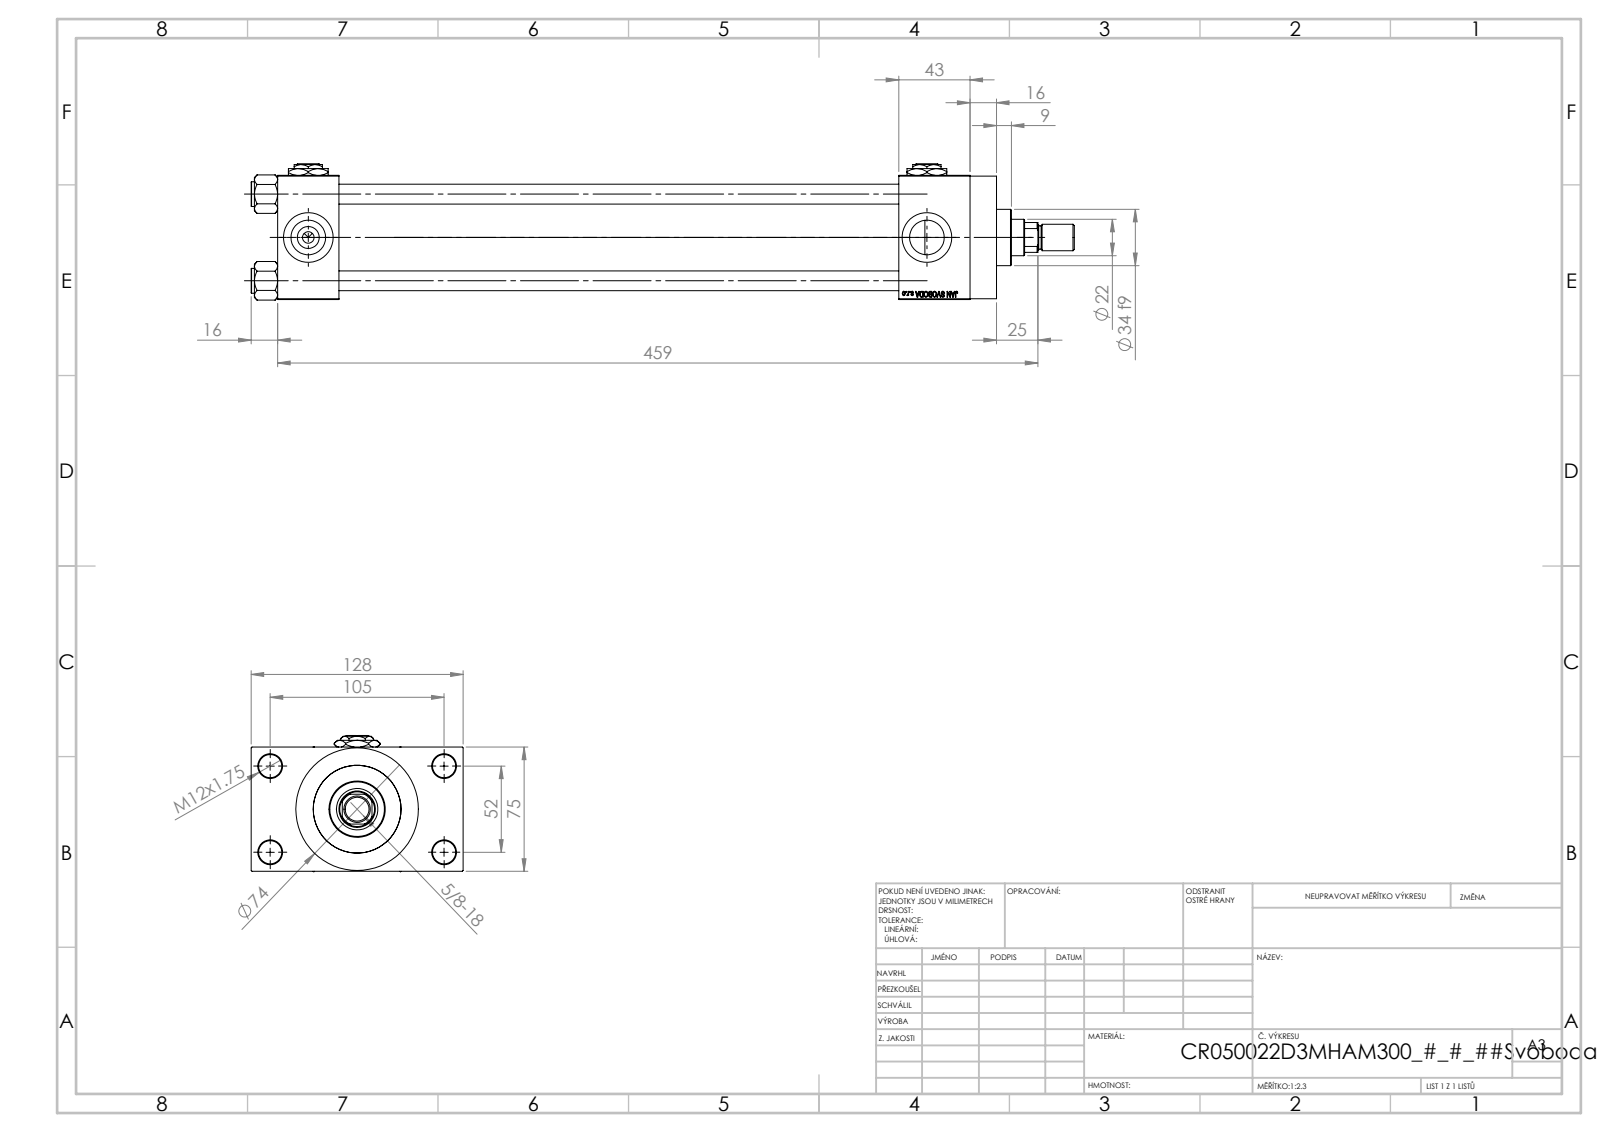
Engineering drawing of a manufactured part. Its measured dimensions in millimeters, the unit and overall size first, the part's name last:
Units: millimetres
Overall size (bounding box): 497 × 128 × 82.27
Round holes (diameter × count): ⌀12 ×4, ⌀14 ×4, ⌀20.96 ×4, ⌀30 ×4, ⌀7 ×3, ⌀10.5 ×1, ⌀22 ×1, ⌀25 ×1, ⌀41 ×1, ⌀50 ×1, ⌀53 ×1
Round bosses / shafts (diameter × count): ⌀15 ×4, ⌀74 ×1, ⌀56 ×1, ⌀34 ×1, ⌀16 ×1, ⌀14 ×1
Partial cylindrical surfaces — rounded edges, fillets, slot ends (radius × count): R10.5 ×1
Main face-to-face distances: 75, 338, 37, 375, 26.5, 418, 381, 43, 101.5, 16
Hole centre spacings: 26.35, 36.98, 52.3, 58.43, 58.59, 78.65, 94.37, 52
Volume: 1 170 000 mm³ · Surface area: 327 280 mm²
Bodies: 14 solids, 1218 faces (549 planar, 103 cylindrical, 566 other)
Part name (STEP PRODUCT): ROD_END_AH; V215_VC_A; Zatka_pro_OIL_PORT; V215CR_D_Body (+3 more)
STEP written by: SolidWorks 2019 (CONFIG_CONTROL_DESIGN)
